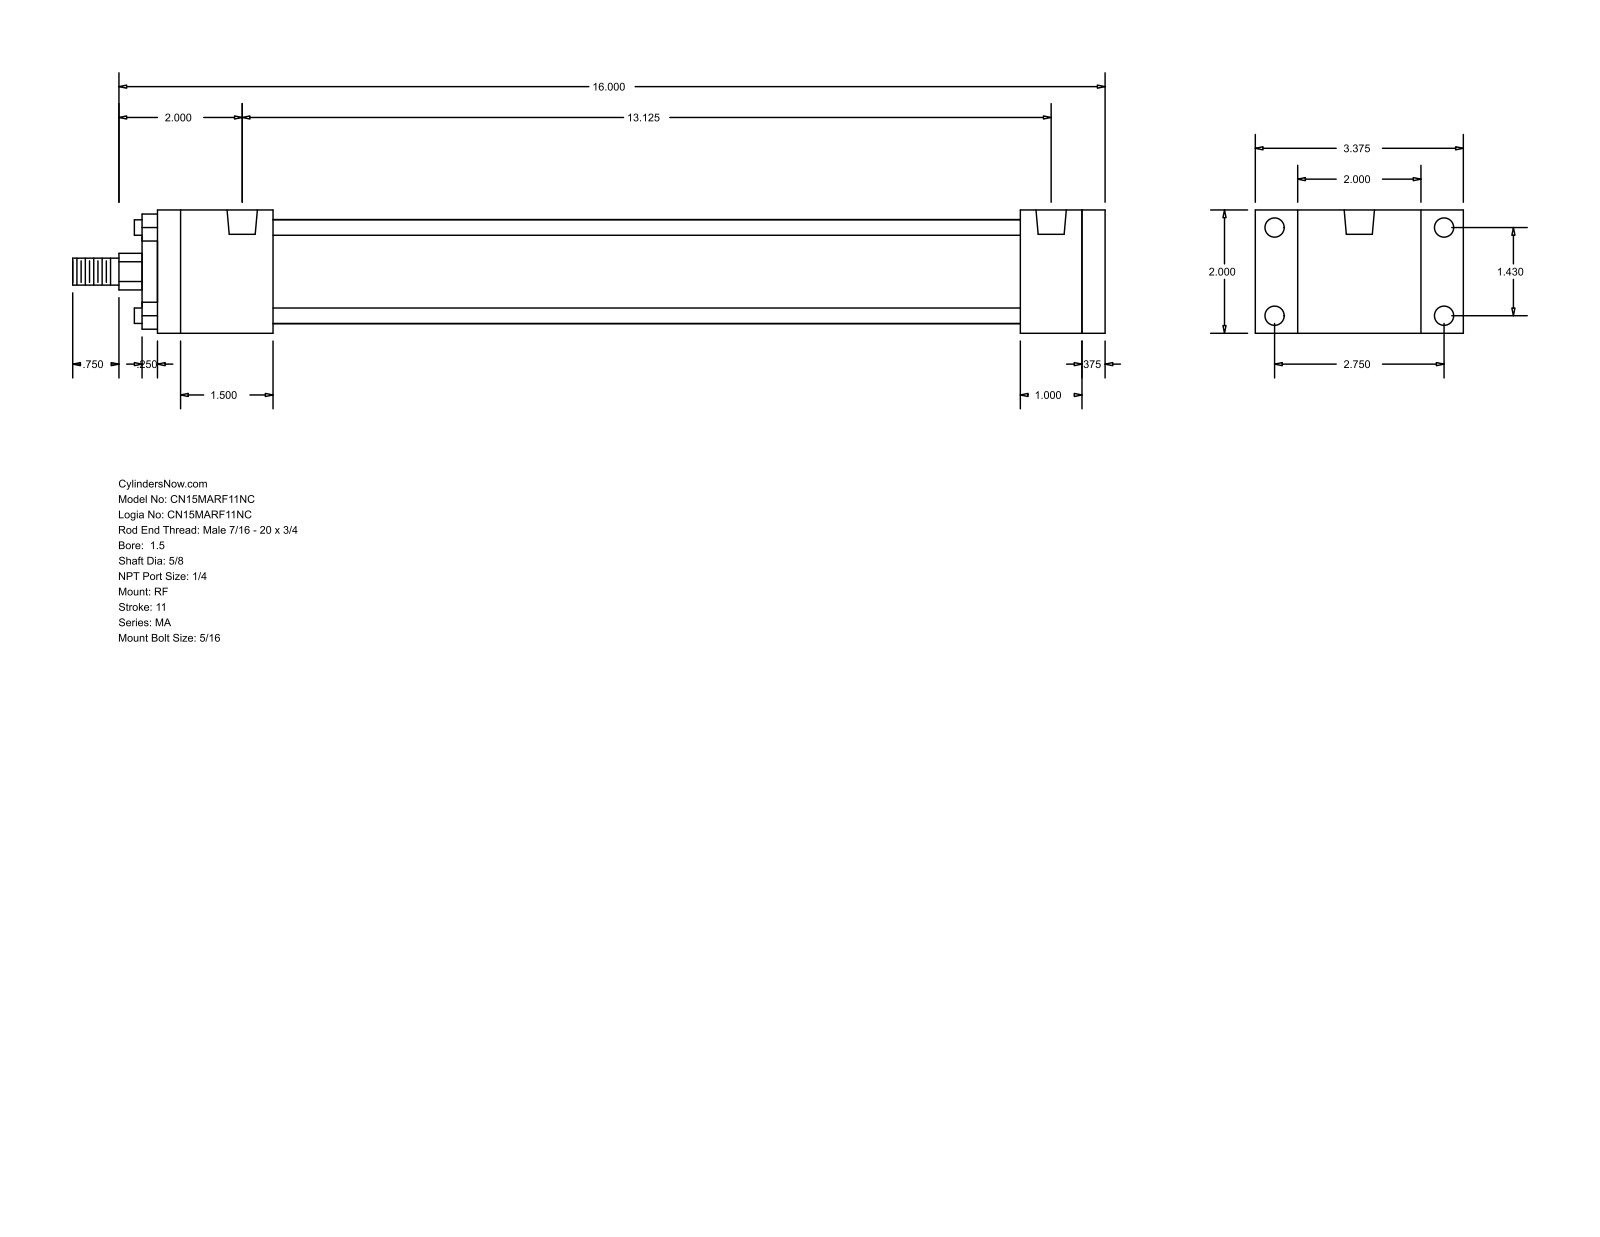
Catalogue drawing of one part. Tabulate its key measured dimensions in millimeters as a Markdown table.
| quantity | value |
| --- | --- |
| part name | MA_RF__0150_0.625 |
| STEP written by | GSSL Pune (CONFIG_CONTROL_DESIGN) |
| units | millimeters |
| bodies | 0 solids, 92 faces (64 planar, 28 cylindrical, 0 other) |
| overall size | 425.45 × 85.72 × 50.8 |
| round holes (diameter × count) | 7.94 × 8, 12.49 × 2 |
| round bosses / shafts (diameter × count) | 6.35 × 4, 42.93 × 1, 28.57 × 1, 15.88 × 1, 11.11 × 1 |
| partial cylindrical surfaces (radius × count) | 7.54 × 1 |
| main face-to-face distances | 50.8, 9.52, 381, 390.52, 25.4, 355.6, 34.92, 47.62, 307.98, 333.38 |
| hole center spacings | 36.32, 69.84, 78.72, 333.38 |
